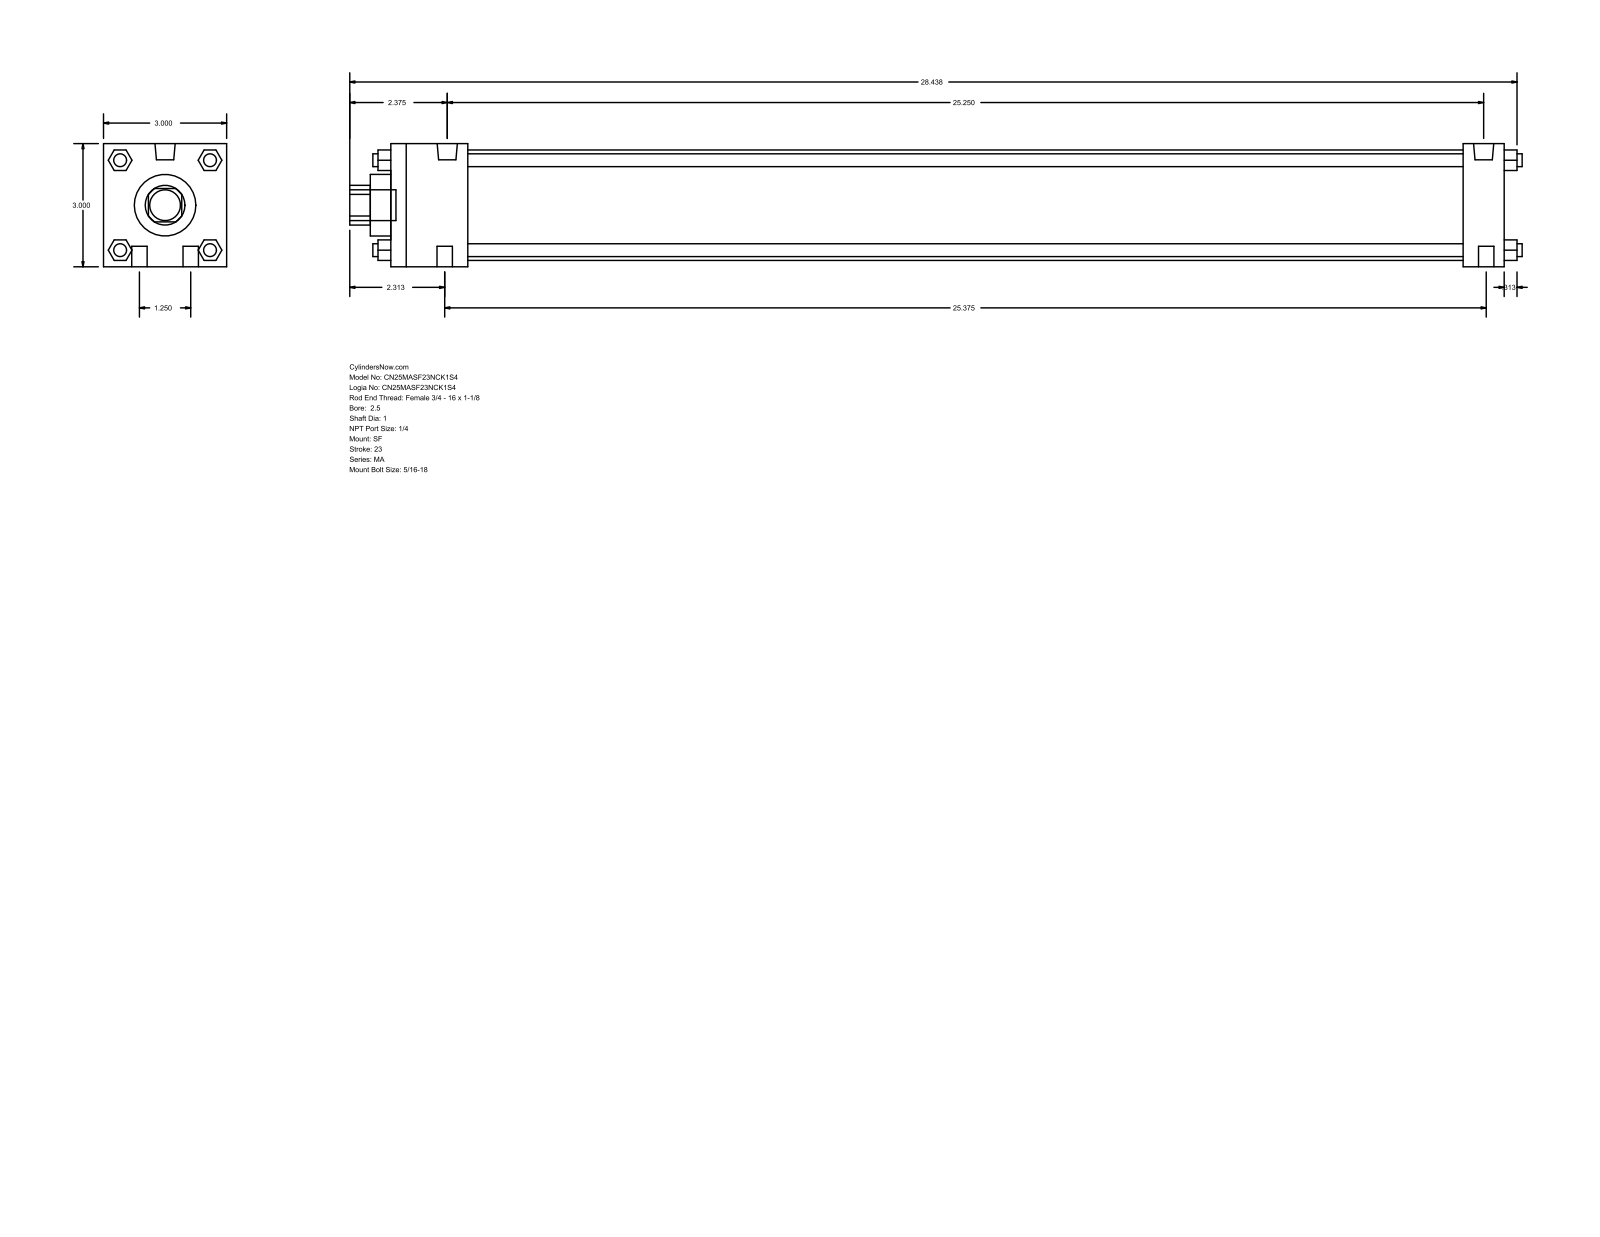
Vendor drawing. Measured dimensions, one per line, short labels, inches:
name: MA_SF__0250_1
written by: GSSL Pune (CONFIG_CONTROL_DESIGN)
unit: in
bodies: 0 solids, 124 faces (94 planar, 30 cylindrical, 0 other)
size: 28.563 × 3 × 3
holes: 1× ⌀1, 1× ⌀1.5, 1× ⌀2.69
bosses: 6× ⌀0.313, 4× ⌀0.375, 2× ⌀0.492, 1× ⌀0.75
rounds: 1× R0.484
face distances: 3, 27.125, 0.5, 1, 26.125, 1.875, 24.25, 25.25, 1.095, 1.896
